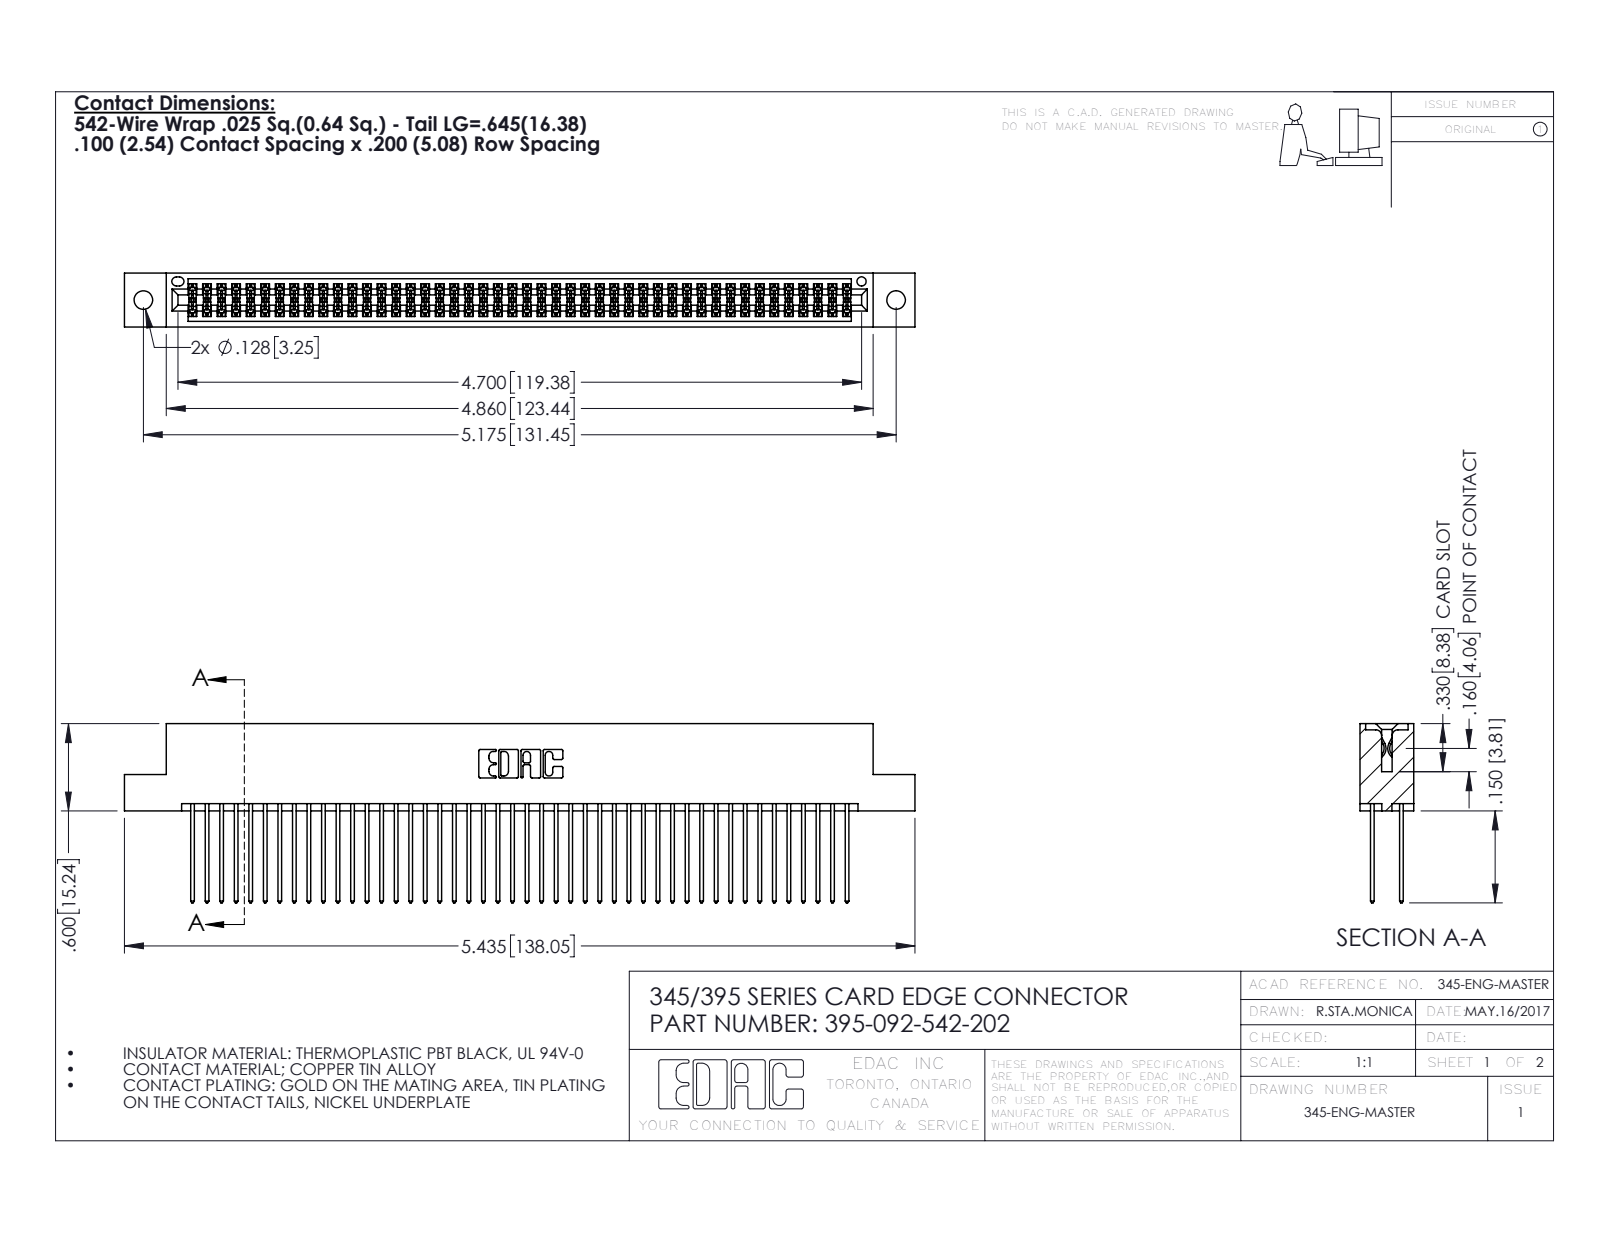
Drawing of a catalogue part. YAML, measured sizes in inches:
part_name: "395-092-542-202; 345 Part_Flush Mounting Lugs - 0.128 Dia; 345-292-001_345-293-142"
step_written_by: "SolidWorks 2016 (CONFIG_CONTROL_DESIGN)"
units: inches
bodies: {solids: 93, faces: 4726, planar: 3116, cylindrical: 1610, other: 0}
overall_size: [5.435, 1.232, 0.37]
volume: 0.845
surface_area: 34.51
round_holes:
  - {diameter: 0.128, count: 2}
  - {diameter: 0.064, count: 1}
partial_cylinders:
  - {radius: 0.006, count: 138}
  - {radius: 0.01, count: 92}
  - {radius: 0.01, count: 22}
  - {radius: 0.007, count: 6}
  - {radius: 0.031, count: 6}
  - {radius: 0.026, count: 3}
  - {radius: 0.014, count: 2}
  - {radius: 0.019, count: 2}
face_to_face_distances: [0.298, 0.072, 0.2, 0.098, 0.272, 0.025, 0.225, 0.37, 0.175, 0.149]
hole_center_spacings: [0.27, 4.939, 5.175]
